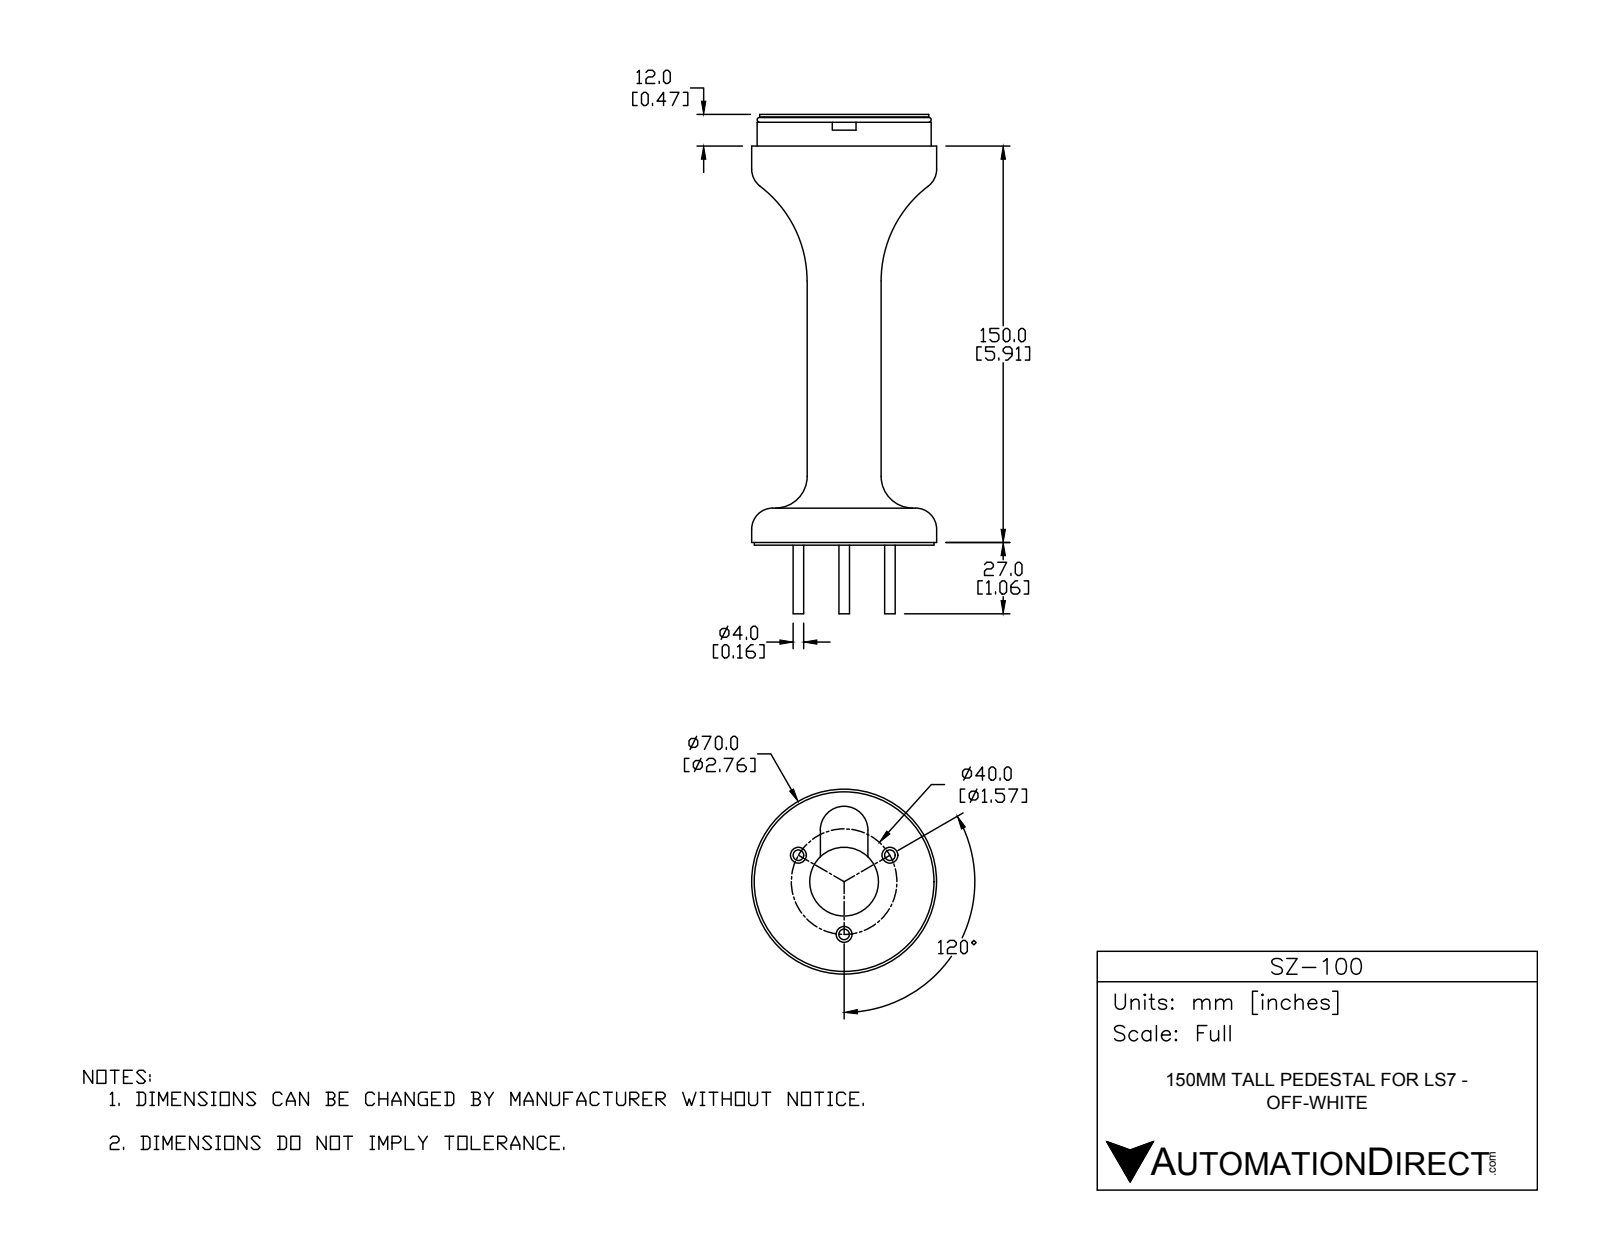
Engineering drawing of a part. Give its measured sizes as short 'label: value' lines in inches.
name: SZ-100
written by: SolidWorks 2016 (AUTOMOTIVE_DESIGN)
unit: in
bodies: 6 solids, 88 faces (31 planar, 35 cylindrical, 22 other)
size: 7.441 × 2.756 × 2.756
volume: 5.684 in³; area: 84.47 in²
holes: 3× ⌀0.236, 1× ⌀1.024, 1× ⌀2.362
bosses: 3× ⌀0.157, 1× ⌀2.756, 1× ⌀2.677, 1× ⌀2.594, 1× ⌀2.52, 1× ⌀2.378, 1× ⌀1.102
rounds: 1× R0.039, 1× R0.354
face distances: 0.039, 6.378, 6.299, 6.26, 0.354, 5.945, 5.906, 0.118, 6.417, 0.472
hole spacings: 0.787, 1.364
